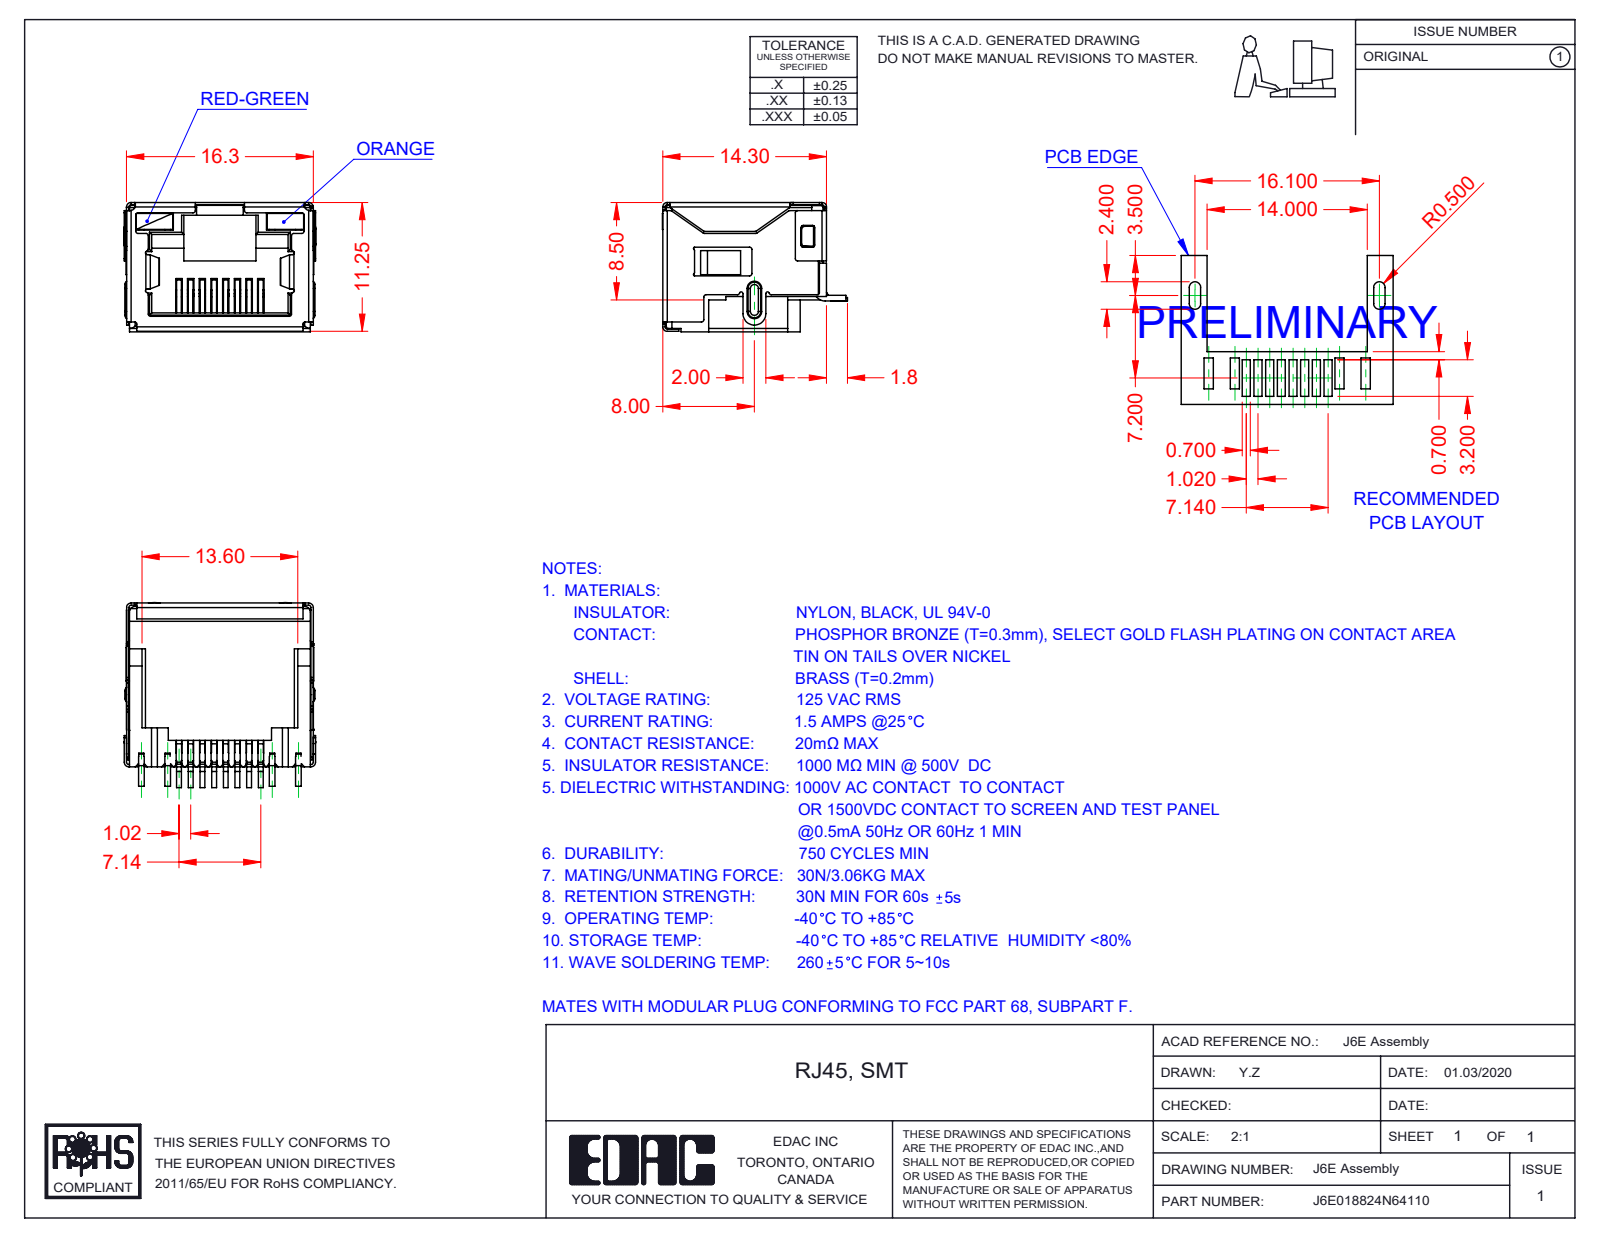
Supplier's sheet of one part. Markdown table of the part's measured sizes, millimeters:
| quantity | value |
| --- | --- |
| part name | J6E018824N64110; 6E LED RH_4-Orange; 6E Contacts; 6E LED LH_6-Red-Green (+2 more) |
| STEP written by | SolidWorks 2016 (CONFIG_CONTROL_DESIGN) |
| units | millimeters |
| bodies | 12 solids, 1498 faces (1099 planar, 349 cylindrical, 50 other) |
| overall size | 16.75 × 16.15 × 11.3 |
| volume | 1 109 mm³ |
| surface area | 4 045 mm² |
| partial cylindrical surfaces (radius × count) | 0.2 × 82, 0.25 × 17, 0.4 × 13, 0.5 × 13, 0.1 × 10, 0.15 × 7, 0.3 × 4, 1 × 3 |
| main face-to-face distances | 11.05, 16.05, 16.1, 15.85, 11.1, 11.3, 2.4, 0.7, 9.85, 0.49 |
